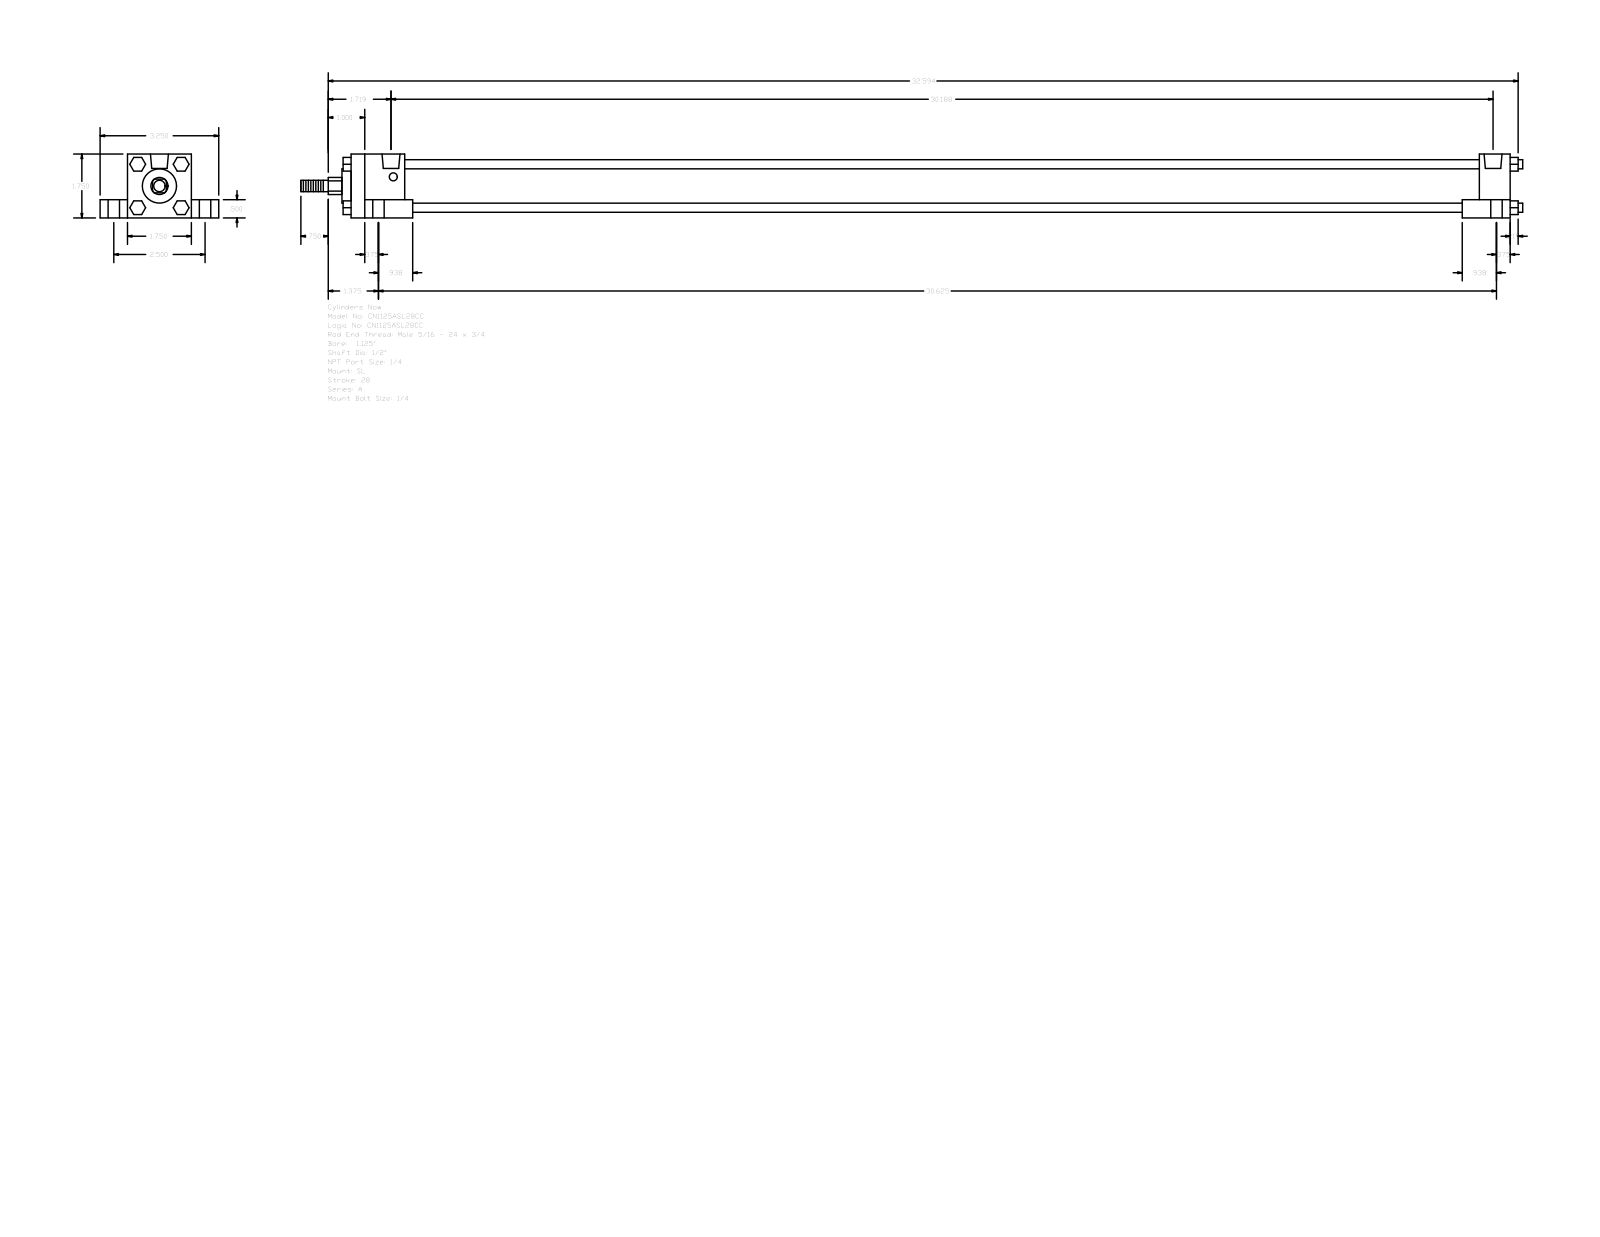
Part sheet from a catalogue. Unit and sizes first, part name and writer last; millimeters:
Units: millimetres
Overall size (bounding box): 850.11 × 82.55 × 44.45
Round holes (diameter × count): ⌀5.56 ×4, ⌀7.94 ×4, ⌀14.29 ×4, ⌀12.49 ×2
Round bosses / shafts (diameter × count): ⌀6.35 ×4, ⌀31.88 ×1, ⌀23.81 ×1, ⌀12.7 ×1, ⌀7.94 ×1
Partial cylindrical surfaces — rounded edges, fillets, slot ends (radius × count): R5.94 ×1
Main face-to-face distances: 44.46, 31.76, 12.7, 19.04, 63.5, 806.45, 785.01, 21.44, 37.3, 747.71
Hole centre spacings: 31.84, 32, 32.93, 33.39, 63.5, 763.59, 768.22, 769.8
Bodies: 0 solids, 150 faces (114 planar, 36 cylindrical, 0 other)
Part name (STEP PRODUCT): A_SL__0112_0.5
STEP written by: GSSL Pune (CONFIG_CONTROL_DESIGN)
